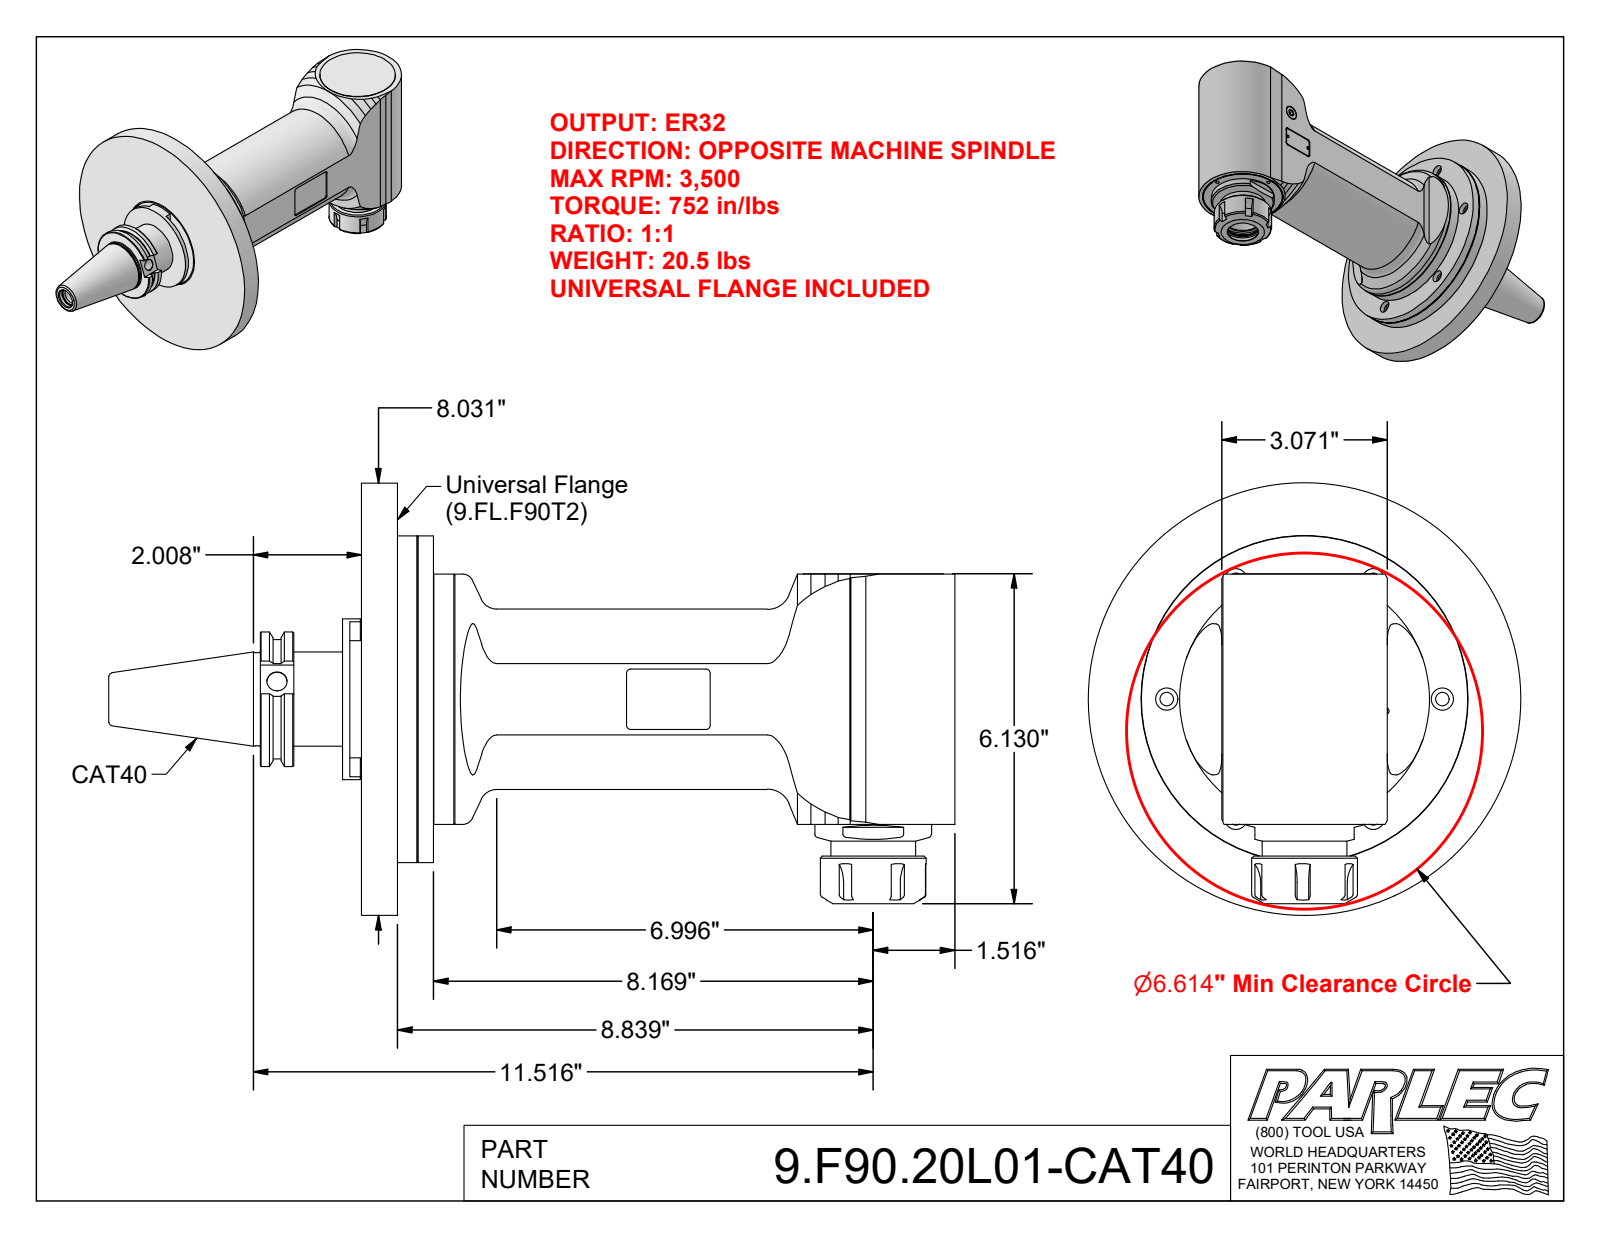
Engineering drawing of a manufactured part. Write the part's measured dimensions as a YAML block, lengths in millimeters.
part_name: "9.F90.20L01-CAT40; 9_F90_20L01; 9_SK_44_2 (EVO, MTC, CAT40); 9_FL_F90T2 (MTC, Universal Flange, Type 2)"
step_written_by: "Autodesk Inventor 2022 (AUTOMOTIVE_DESIGN)"
units: millimeters
bodies: {solids: 5, faces: 368, planar: 166, cylindrical: 106, other: 96}
overall_size: [399.3, 204, 204]
volume: 2671000
surface_area: 294800
round_holes:
  - {diameter: 10.4, count: 10}
  - {diameter: 6.4, count: 6}
  - {diameter: 3.2, count: 4}
  - {diameter: 9.5, count: 1}
  - {diameter: 12.5, count: 1}
  - {diameter: 13.4, count: 1}
  - {diameter: 16.3, count: 1}
  - {diameter: 16.8, count: 1}
  - {diameter: 20, count: 1}
  - {diameter: 24, count: 1}
  - {diameter: 27, count: 1}
  - {diameter: 29.5, count: 1}
round_bosses_or_shafts:
  - {diameter: 10, count: 4}
  - {diameter: 6, count: 4}
  - {diameter: 2.5, count: 2}
  - {diameter: 204, count: 1}
  - {diameter: 154.2, count: 1}
  - {diameter: 154, count: 1}
  - {diameter: 121.4, count: 1}
  - {diameter: 118, count: 1}
partial_cylinders:
  - {radius: 2, count: 12}
  - {radius: 4, count: 6}
  - {radius: 15, count: 6}
  - {radius: 38, count: 1}
  - {radius: 42.5, count: 1}
face_to_face_distances: [17, 34, 3.5, 9, 78, 13.5, 30.5, 22.5, 5.5, 39.5]
hole_center_spacings: [65, 112.6, 21.7, 31.5, 44.6, 46.1, 49, 69.3]
